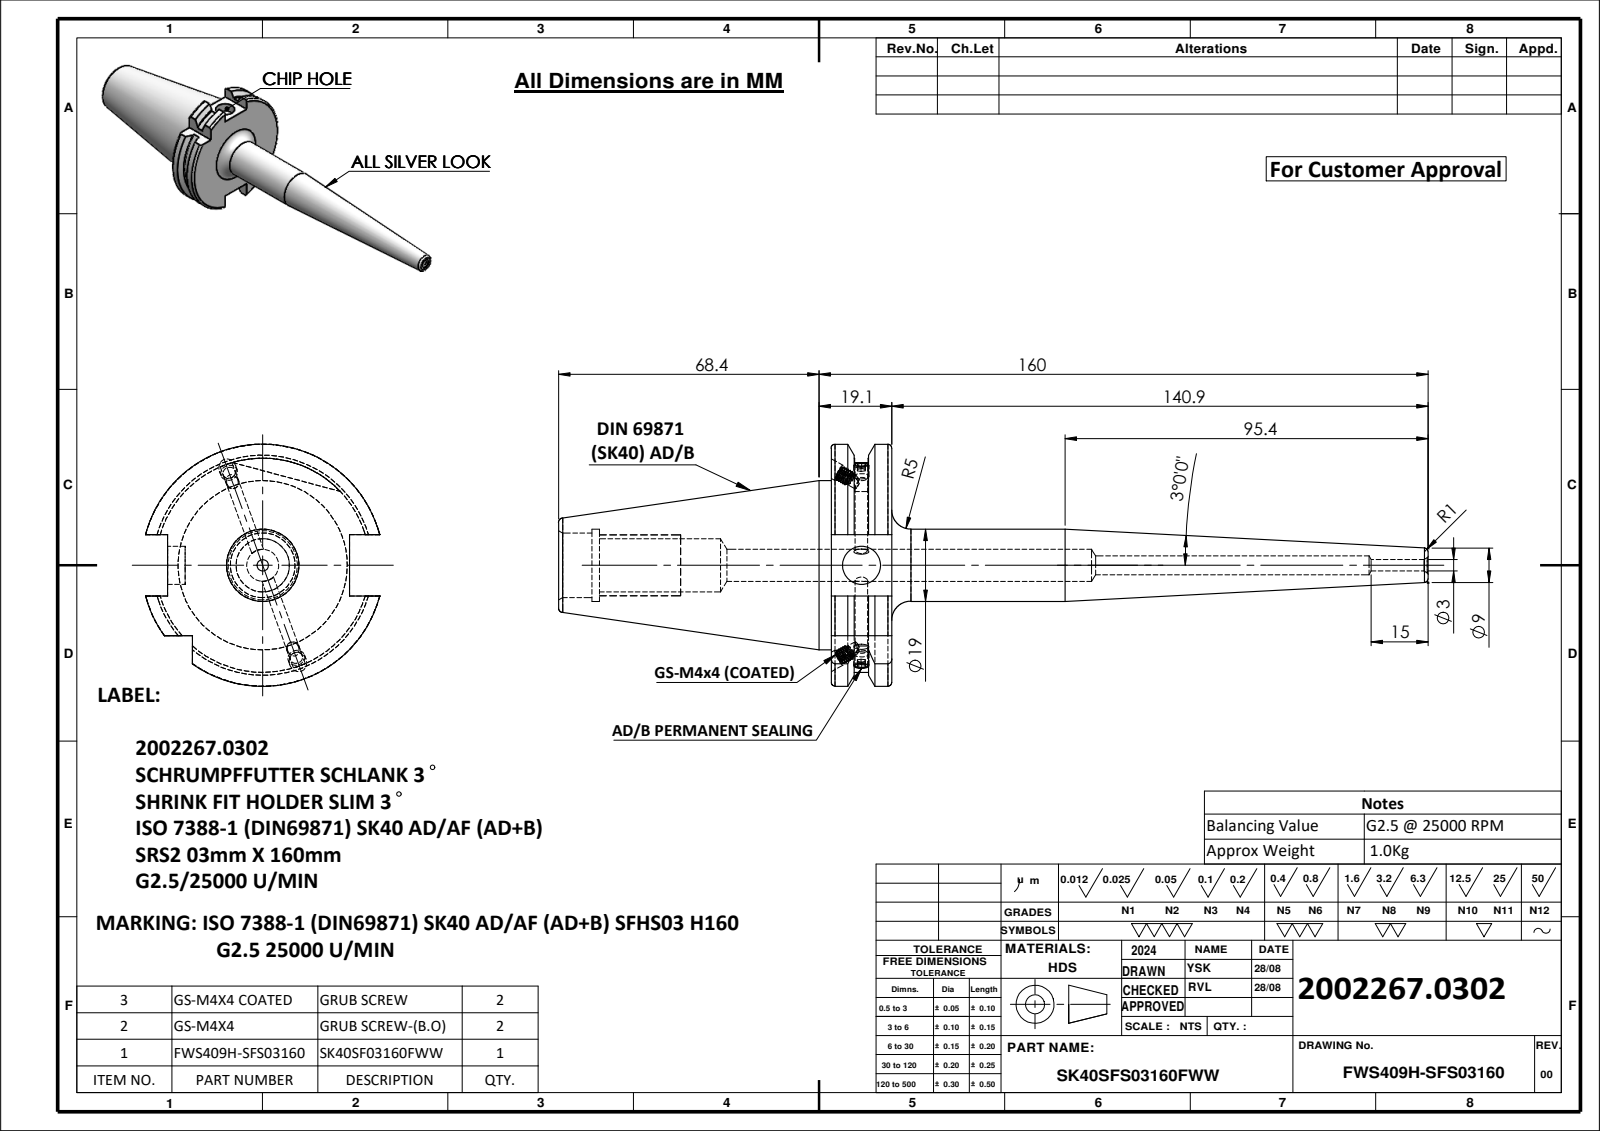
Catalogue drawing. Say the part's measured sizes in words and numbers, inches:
The part is named "FWS409H-SFS03160; GS-M4X4_DIN 913 - M4 x 4-N; SK40SFS03160FWW; GS-M4X4-COATING_DIN 913 - M4 x 4-N". Its 3-D file was written by "SolidWorks 2024 (CONFIG_CONTROL_DESIGN)". It is 5 solids with 244 faces: 62 planar, 70 cylindrical and 112 other. Overall it measures 8.992 by 2.502 by 2.42 inches. Its volume is 7.741 cubic inches and its surface area 47.06 square inches. Round holes: 3 of diameter 0.13, 2 of diameter 0.177, 1 of diameter 0.118, 1 of diameter 0.197, 1 of diameter 0.331, 1 of diameter 0.394, 1 of diameter 0.551, 1 of diameter 0.669, 1 of diameter 0.748. Round bosses or shafts: 4 of diameter 0.157, 2 of diameter 0.114, 1 of diameter 1.75. Partial cylindrical surfaces (rounded edges, fillets, slot ends): 1 of radius 1.107, 1 of radius 1.251. The main face-to-face distances are 0.626, 0.634, 1.882, 2.819, 3.445, 0.421, 2.398, 3.024, 3.056, 2.635.
